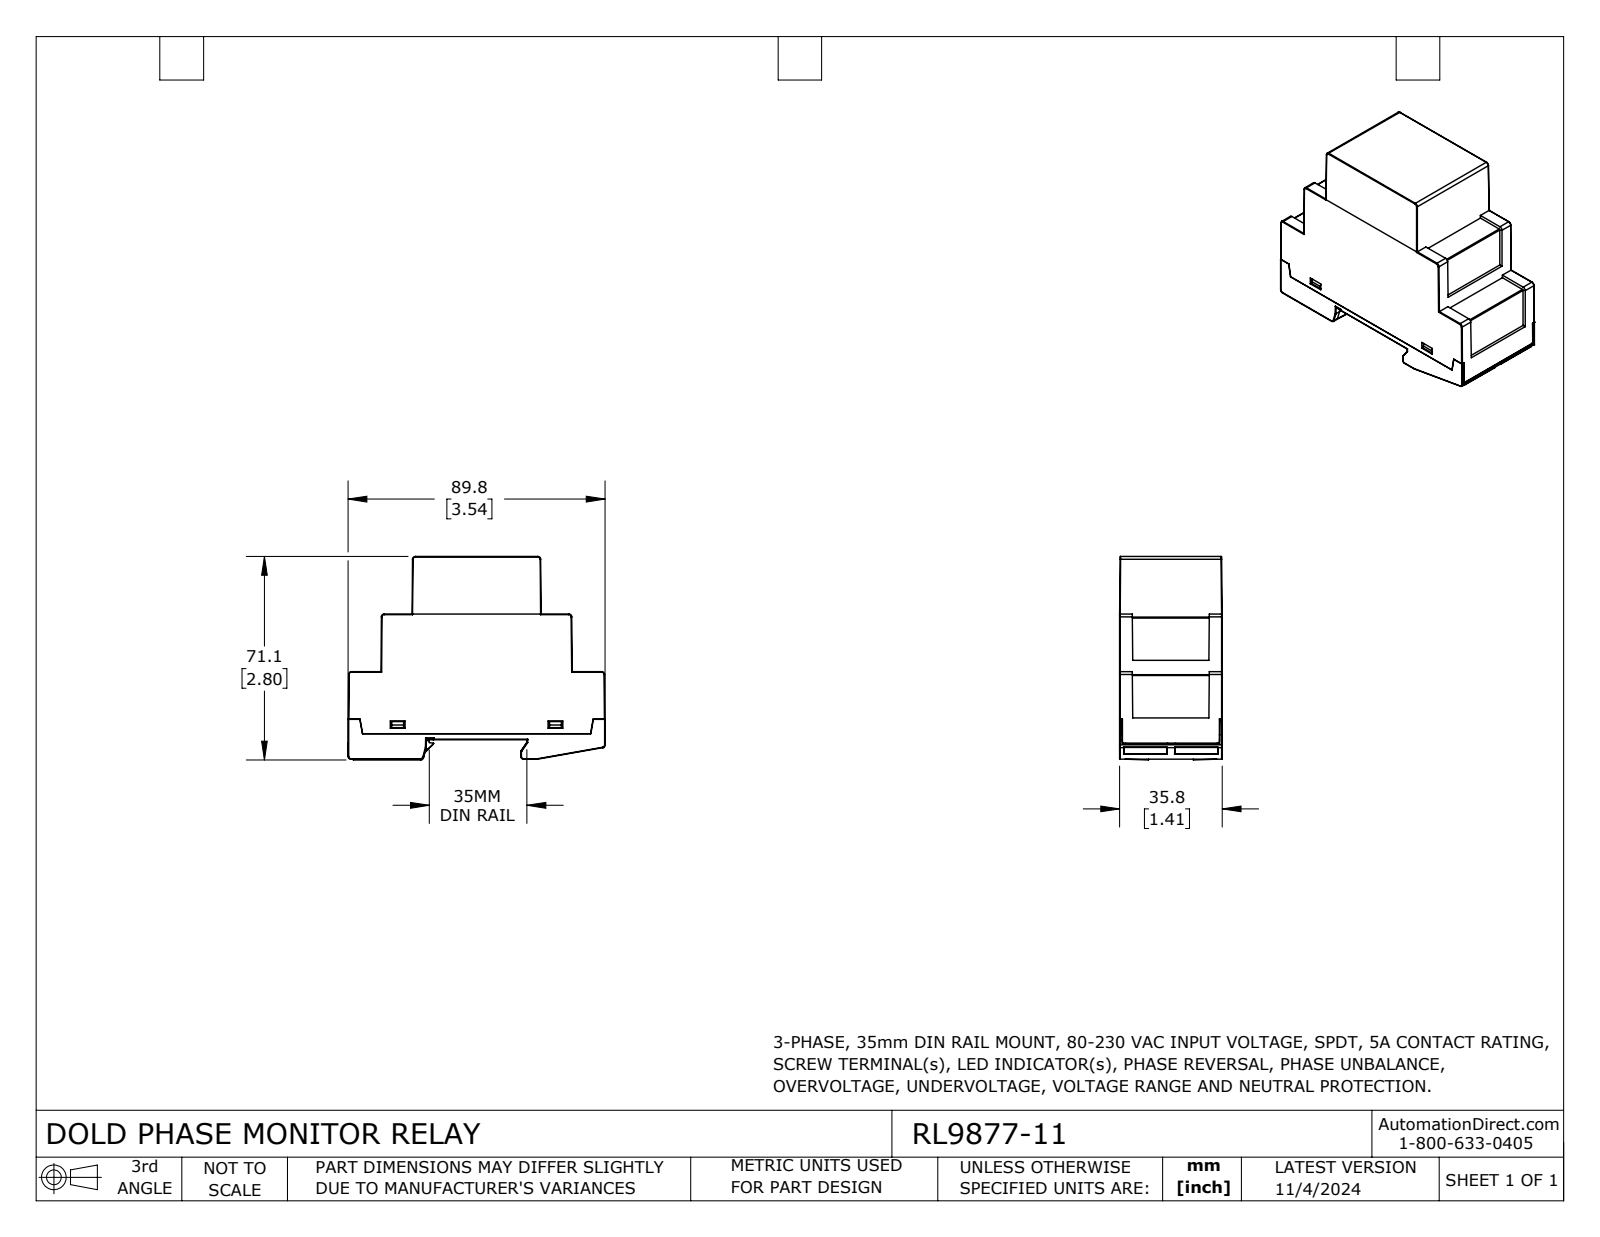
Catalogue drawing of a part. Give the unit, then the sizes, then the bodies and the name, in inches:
Units: inches
Overall size (bounding box): 3.538 × 2.799 × 1.409
Round bosses / shafts (diameter × count): ⌀0.098 ×2, ⌀0.315 ×1
Partial cylindrical surfaces — rounded edges, fillets, slot ends (radius × count): R0.008 ×42, R0.039 ×14, R0.02 ×11, R0.004 ×6, R0.012 ×4, R0.011 ×1, R0.016 ×1, R0.028 ×1
Main face-to-face distances: 1.409, 0.217, 2.52, 0.035, 0.085, 2.435, 2.219, 0.301, 0.824, 1.374
Volume: 9.341 in³ · Surface area: 55.26 in²
Bodies: 2 solids, 631 faces (484 planar, 109 cylindrical, 38 other)
Part name (STEP PRODUCT): RL9877-11
STEP written by: SolidWorks 2023 (CONFIG_CONTROL_DESIGN)
